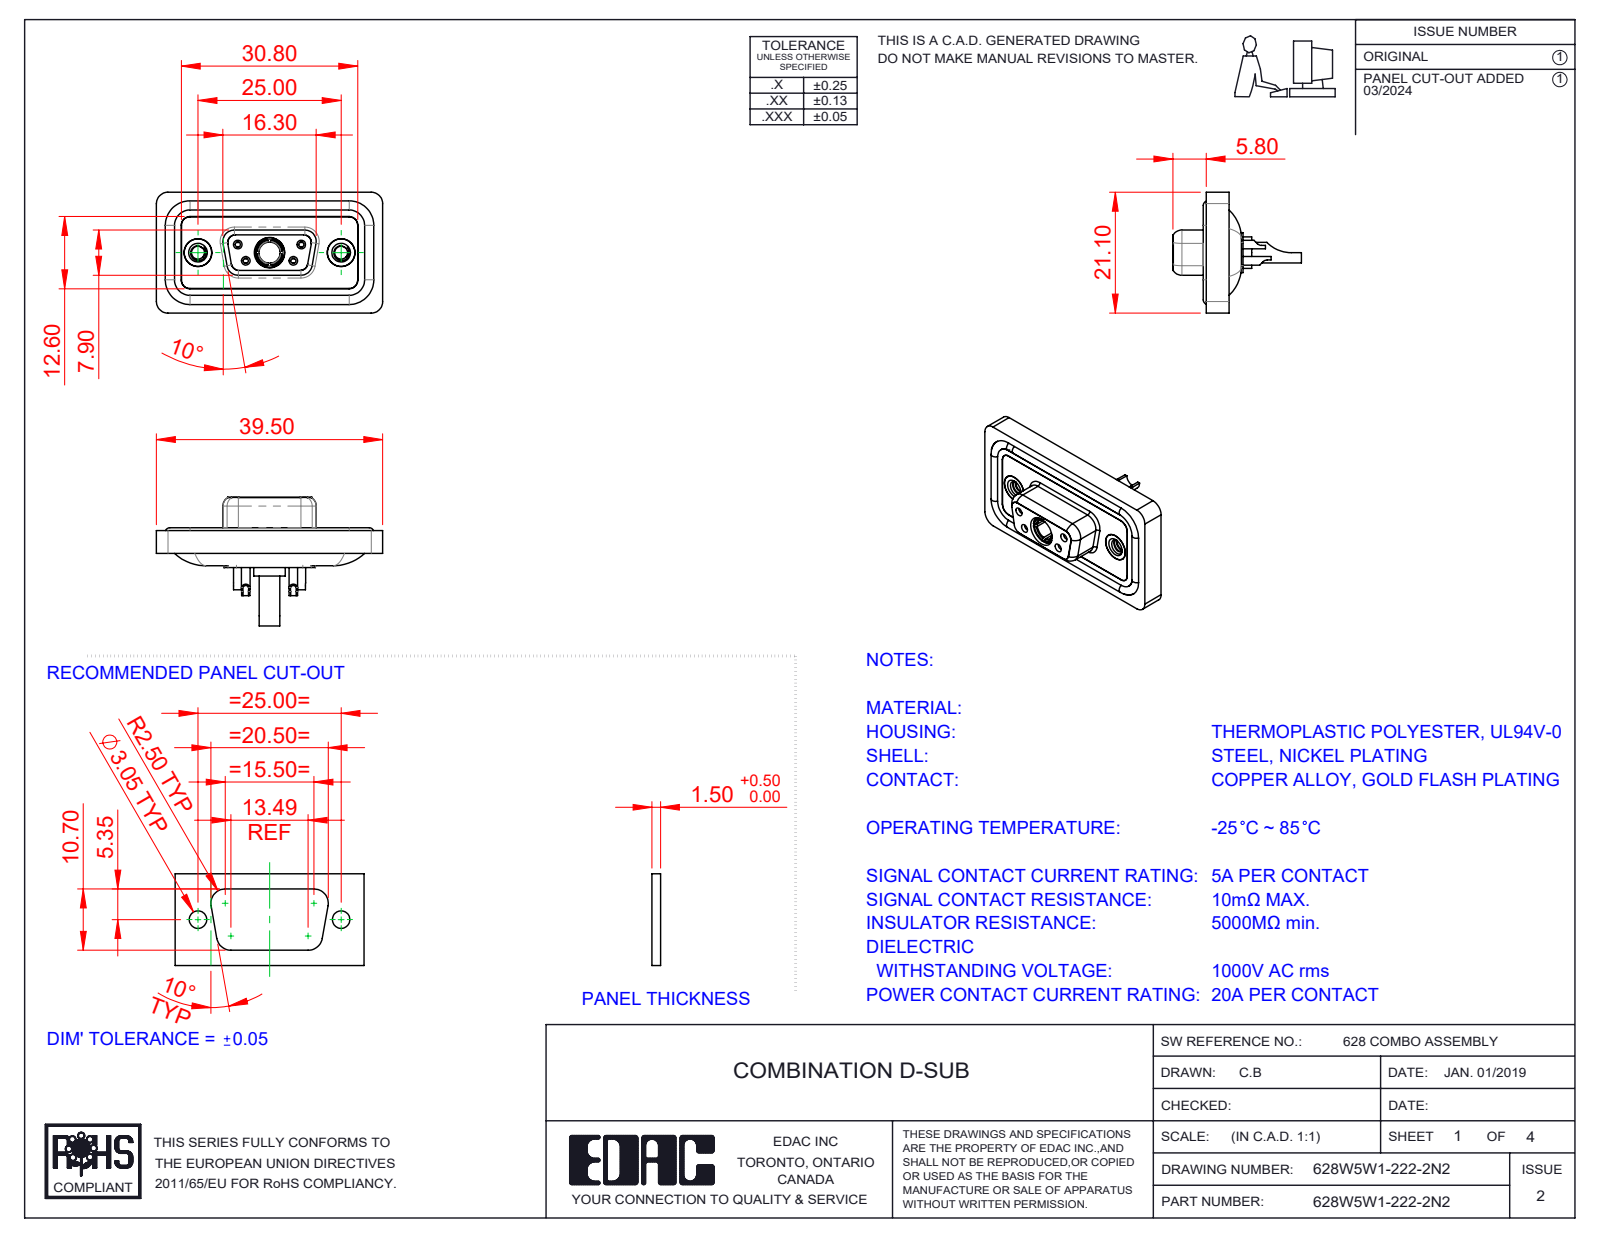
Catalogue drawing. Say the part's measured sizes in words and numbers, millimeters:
The part is named "628W5W1-222-2N2; 628Combo Housing_5W1; 628Combo Shell Front_09 Contacts; 628Combo Waterproof Housing_09 Contacts (+5 more)". Its 3-D file was written by "SolidWorks 2023 (CONFIG_CONTROL_DESIGN)". It is 13 solids with 686 faces: 205 planar, 298 cylindrical and 183 other. Overall it measures 39.5 by 22.45 by 21.1 millimeters. Its volume is 4 788 cubic millimeters and its surface area 7 760 square millimeters. Round holes: 4 of diameter 0.9, 4 of diameter 1, 4 of diameter 1.1, 4 of diameter 1.5, 4 of diameter 2, 3 of diameter 4.85, 2 of diameter 1.6, 2 of diameter 1.7, 2 of diameter 2.26, 2 of diameter 4, 2 of diameter 4.05, 2 of diameter 5. Round bosses or shafts: 6 of diameter 1.6, 4 of diameter 2.2, 2 of diameter 4.95, 2 of diameter 4.8, 1 of diameter 5.5, 1 of diameter 5.2, 1 of diameter 4.96, 1 of diameter 4.75. Partial cylindrical surfaces (rounded edges, fillets, slot ends): 22 of radius 1.5, 18 of radius 2, 8 of radius 1.35, 8 of radius 1.6, 6 of radius 1, 4 of radius 0.25, 4 of radius 0.5, 4 of radius 0.6. The main face-to-face distances are 0.4, 2.9, 1.1, 1.8, 1.6, 0.5, 5.65, 7.45, 5.35, 3.6. The hole center spacings are 3.16, 5.72, 7.1, 12.5, 18.1, 4.39, 4.4, 8.31.
